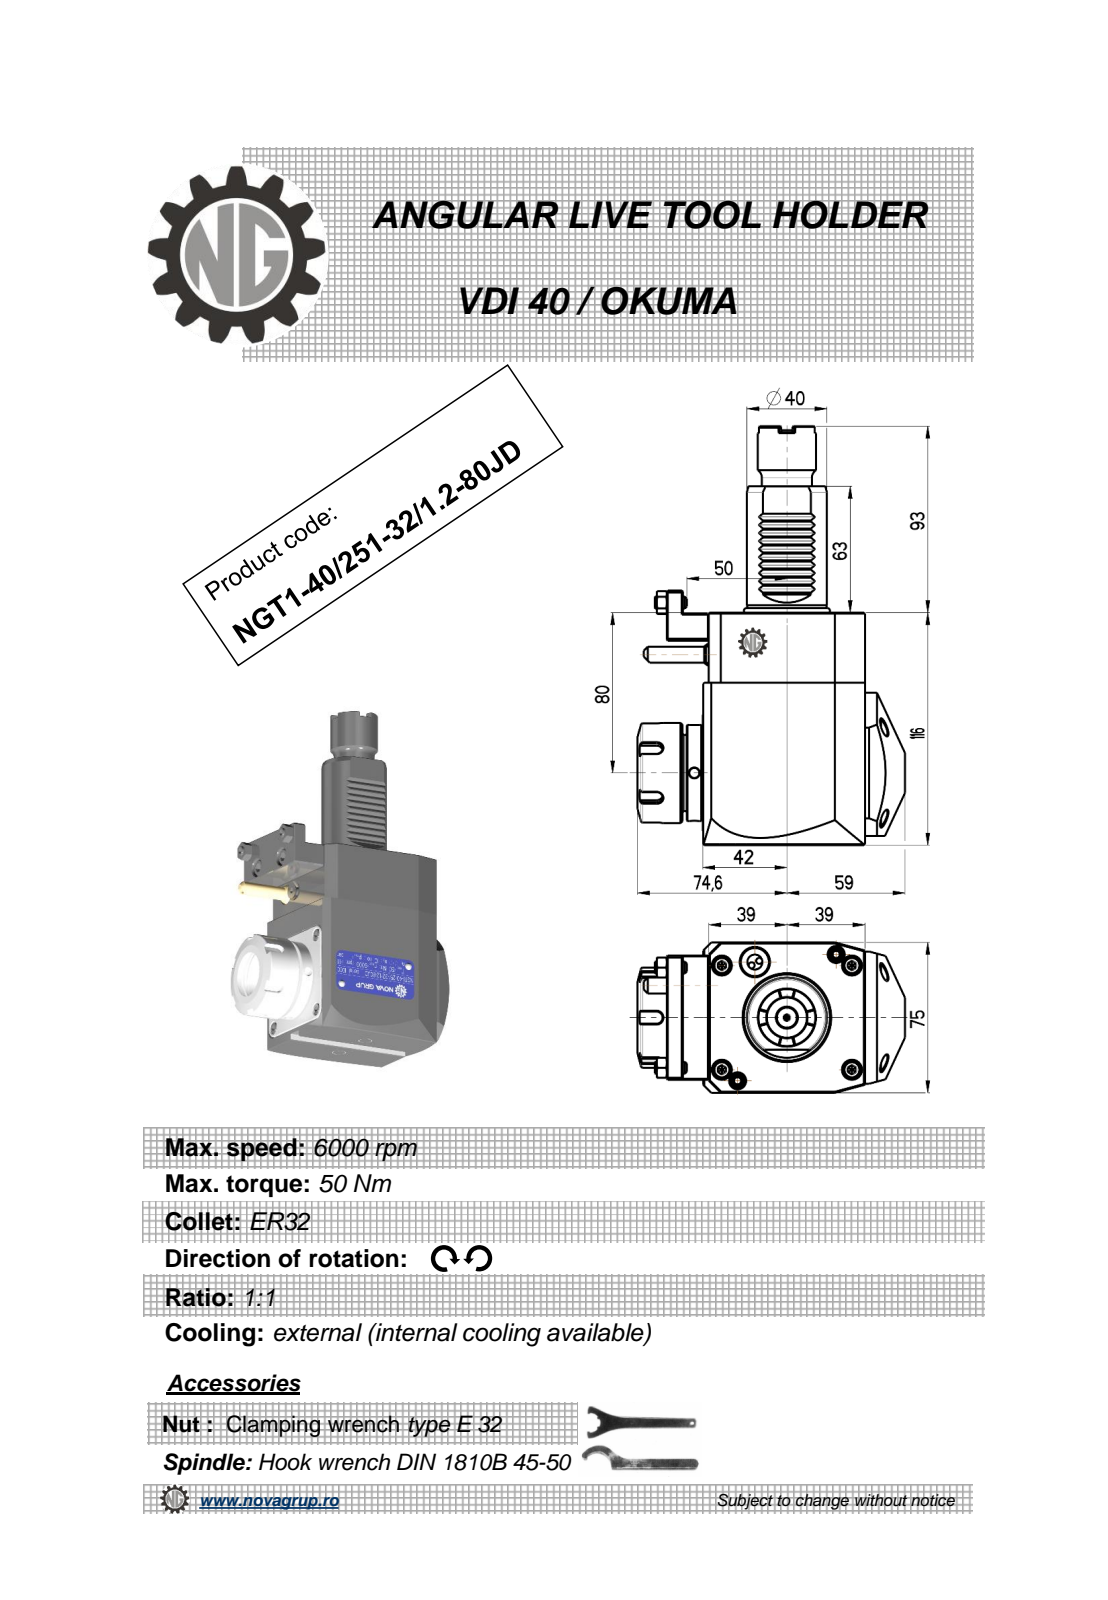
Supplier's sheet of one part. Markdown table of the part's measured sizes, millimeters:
| quantity | value |
| --- | --- |
| part name | NGT1_40_251_32_1_2_80JD |
| STEP written by | PRO/ENGINEER BY PARAMETRIC TECHNOLOGY CORPORATION, 2010280 (CONFIG_CONTROL_DESIGN) |
| units | millimeters |
| bodies | 1 solid, 450 faces (189 planar, 86 cylindrical, 175 other) |
| overall size | 209 × 133.6 × 76.6 |
| volume | 910 627 mm³ |
| surface area | 74 644 mm² |
| round holes (diameter × count) | 5 × 3, 3 × 1, 27 × 1 |
| round bosses / shafts (diameter × count) | 6 × 2, 50 × 1, 48 × 1, 41 × 1, 40 × 1, 29 × 1, 25 × 1, 10 × 1 |
| partial cylindrical surfaces (radius × count) | 0.3 × 10, 0.31 × 10, 0.2 × 6, 3 × 5, 0.5 × 1, 10 × 1, 40 × 1 |
| main face-to-face distances | 75, 116, 81, 0.5, 18, 21, 80.8, 10, 14, 3 |
| hole center spacings | 61.13 |
